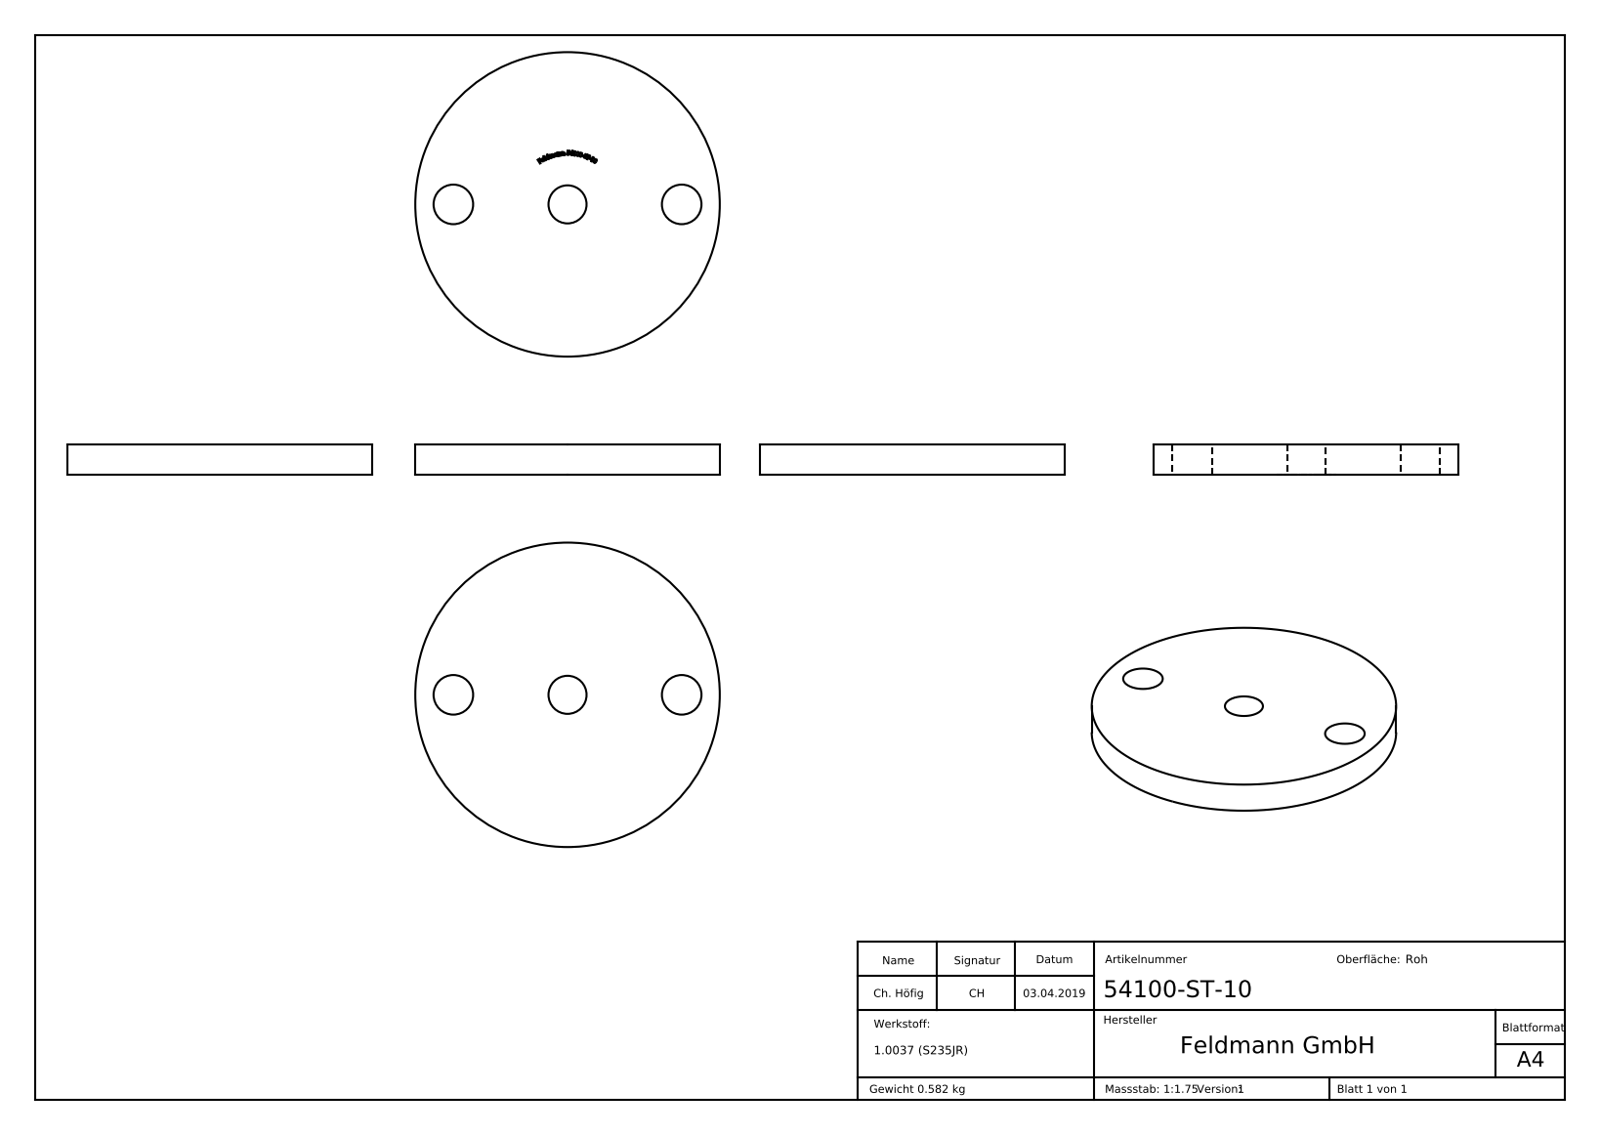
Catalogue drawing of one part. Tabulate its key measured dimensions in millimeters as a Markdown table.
| quantity | value |
| --- | --- |
| part name | 54100-ST-10 |
| STEP written by | SolidWorks 2015 (CONFIG_CONTROL_DESIGN) |
| units | millimeters |
| bodies | 1 solid, 237 faces (131 planar, 8 cylindrical, 98 other) |
| overall size | 100 × 100 × 10 |
| volume | 74 657 mm³ |
| surface area | 19 292 mm² |
| round holes (diameter × count) | 13 × 2, 12.5 × 1 |
| round bosses / shafts (diameter × count) | 100 × 1 |
| main face-to-face distances | 10, 9.9, 0.54, 0.85, 0.72, 0.67, 0.73, 0.6, 0.41, 1.2 |
| hole center spacings | 37.5, 75 |
